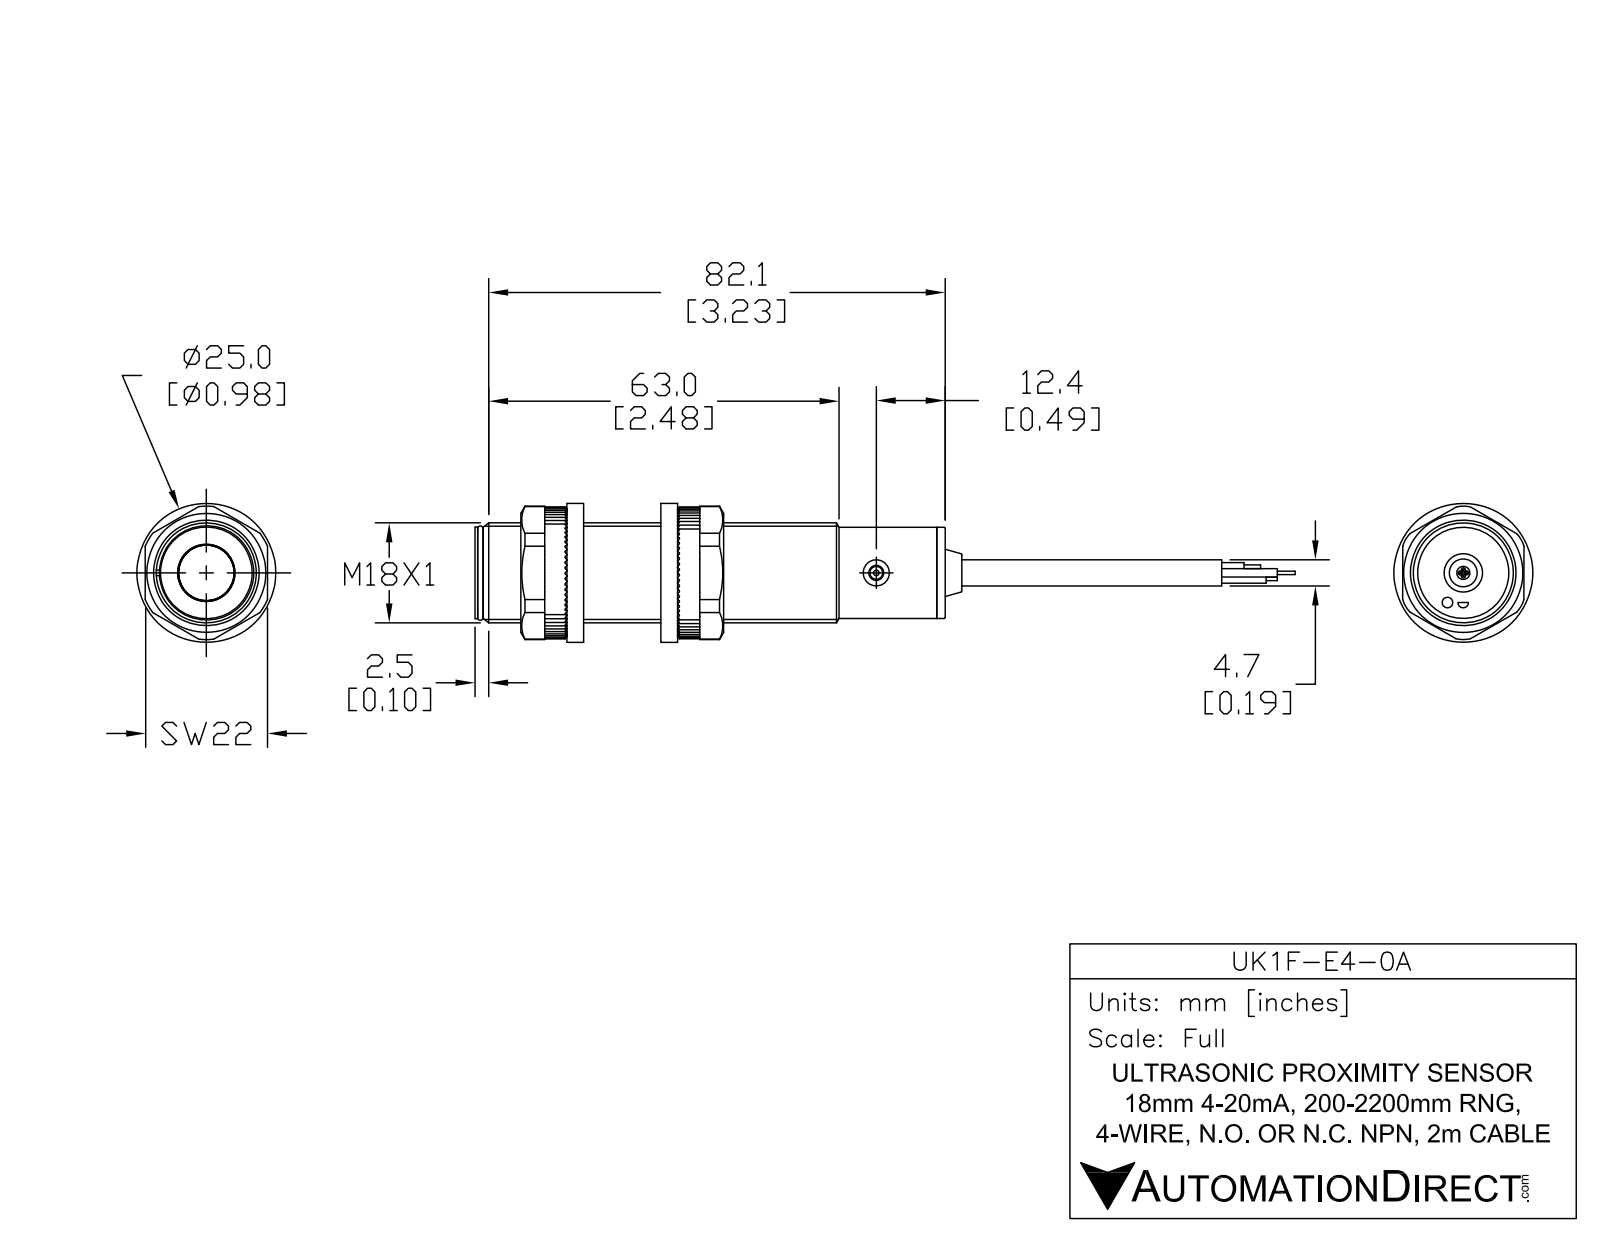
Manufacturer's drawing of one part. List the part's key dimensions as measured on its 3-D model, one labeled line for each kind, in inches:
Part name (STEP PRODUCT): UK1F-E4-0A
STEP written by: SolidWorks 2017 (AUTOMOTIVE_DESIGN)
Units: inches
Bodies: 6 solids, 55 faces (17 planar, 24 cylindrical, 14 other)
Overall size (bounding box): 4.832 × 0.709 × 0.709
Volume: 1.285 in³ · Surface area: 10.69 in²
Round holes (diameter × count): ⌀0.185 ×2, ⌀0.106 ×1
Round bosses / shafts (diameter × count): ⌀0.709 ×1, ⌀0.646 ×1, ⌀0.622 ×1, ⌀0.374 ×1, ⌀0.189 ×1, ⌀0.091 ×1
Main face-to-face distances: 3.193, 3.252, 0.059, 0.039, 3.232, 3.291, 0.041, 3.234, 3.293, 3.257
